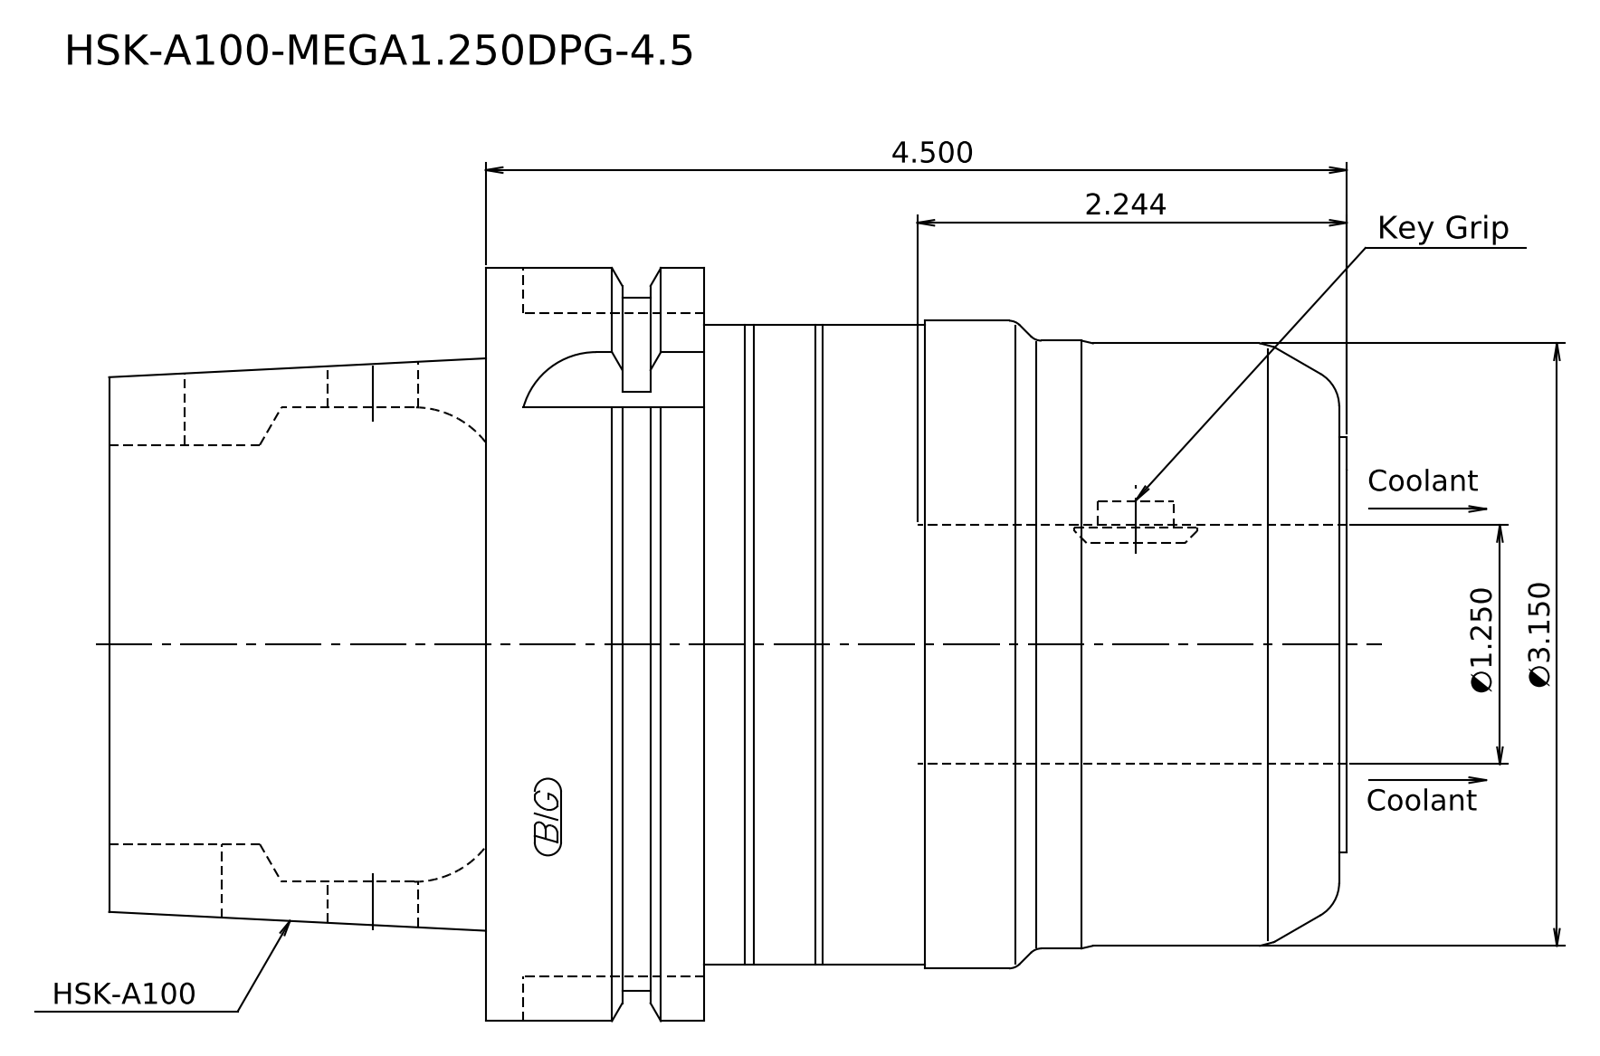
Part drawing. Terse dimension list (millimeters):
written by: Kubotek KeyCreator 2011 V10.0.2 (22737) (automotive_design)
unit: mm
bodies: 1 solid, 23 faces (8 planar, 8 cylindrical, 7 other)
size: 164.3 × 100 × 100
volume: 884 522 mm³; area: 58 222 mm²
bosses: 1× ⌀100, 1× ⌀92, 1× ⌀86, 1× ⌀85, 1× ⌀80.7, 1× ⌀80, 1× ⌀55.1
face distances: 50, 114.3, 164.3, 85.3, 29, 79, 1, 84.3, 113.3, 163.3
